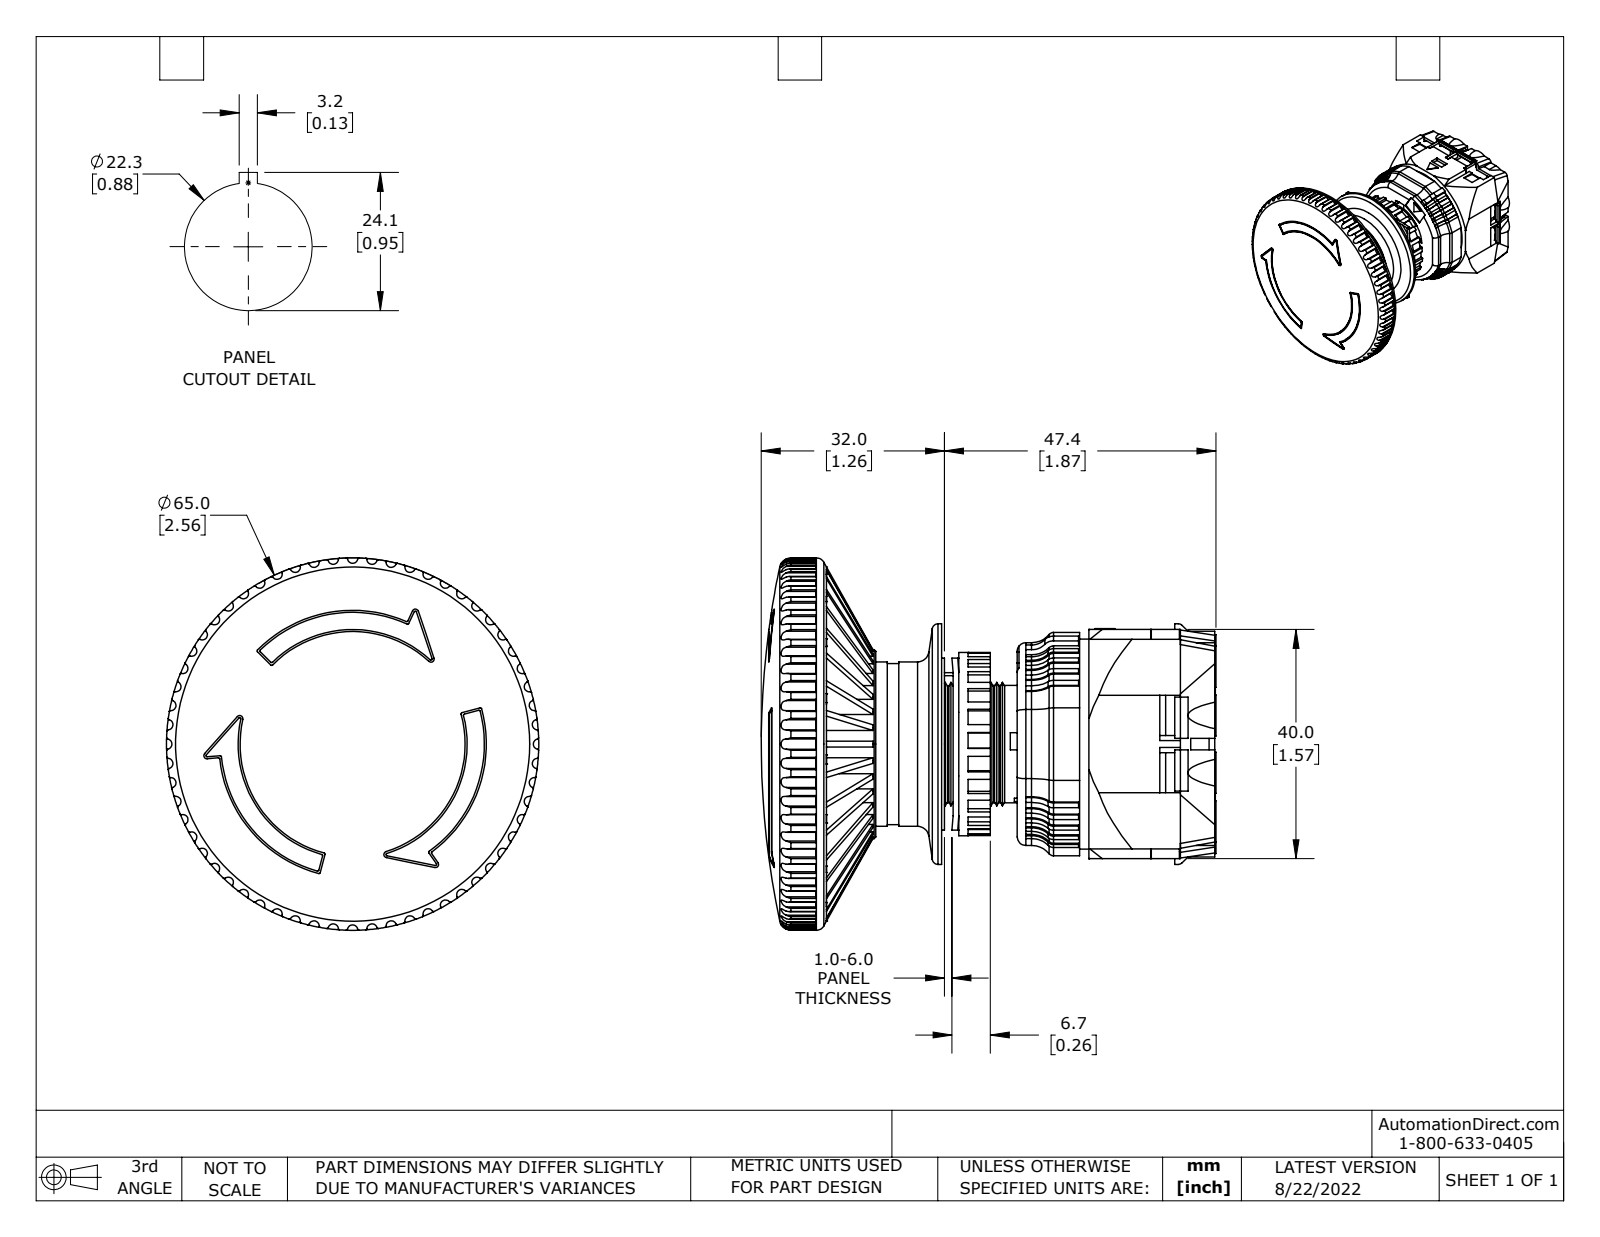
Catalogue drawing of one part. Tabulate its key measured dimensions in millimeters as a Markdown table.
| quantity | value |
| --- | --- |
| part name | AR22VPR-12R |
| STEP written by | SolidWorks 2021 (CONFIG_CONTROL_DESIGN) |
| units | millimeters |
| bodies | 26 solids, 2720 faces (1757 planar, 782 cylindrical, 181 other) |
| overall size | 79.3 × 65 × 65 |
| volume | 71 020 mm³ |
| surface area | 61 370 mm² |
| round holes (diameter × count) | 3.5 × 12, 6.2 × 12, 3.3 × 2, 7 × 1, 8 × 1, 17.5 × 1, 21 × 1, 21.3 × 1, 22 × 1, 22.3 × 1, 28 × 1, 28.1 × 1 |
| round bosses / shafts (diameter × count) | 7.2 × 12, 65 × 1, 42 × 1, 33 × 1, 32 × 1, 30 × 1, 28.7 × 1, 22.4 × 1 |
| partial cylindrical surfaces (radius × count) | 0.2 × 146, 0.9 × 62, 1 × 29, 1.2 × 19, 3.8 × 19, 31.7 × 18, 1.5 × 12, 4.2 × 12 |
| main face-to-face distances | 1, 10, 8, 11.5, 8.6, 36.1, 22, 18, 12.4, 21.5 |
| hole center spacings | 16.3, 23, 8.3, 8.9, 10, 14.9, 18.1, 18.7 |
